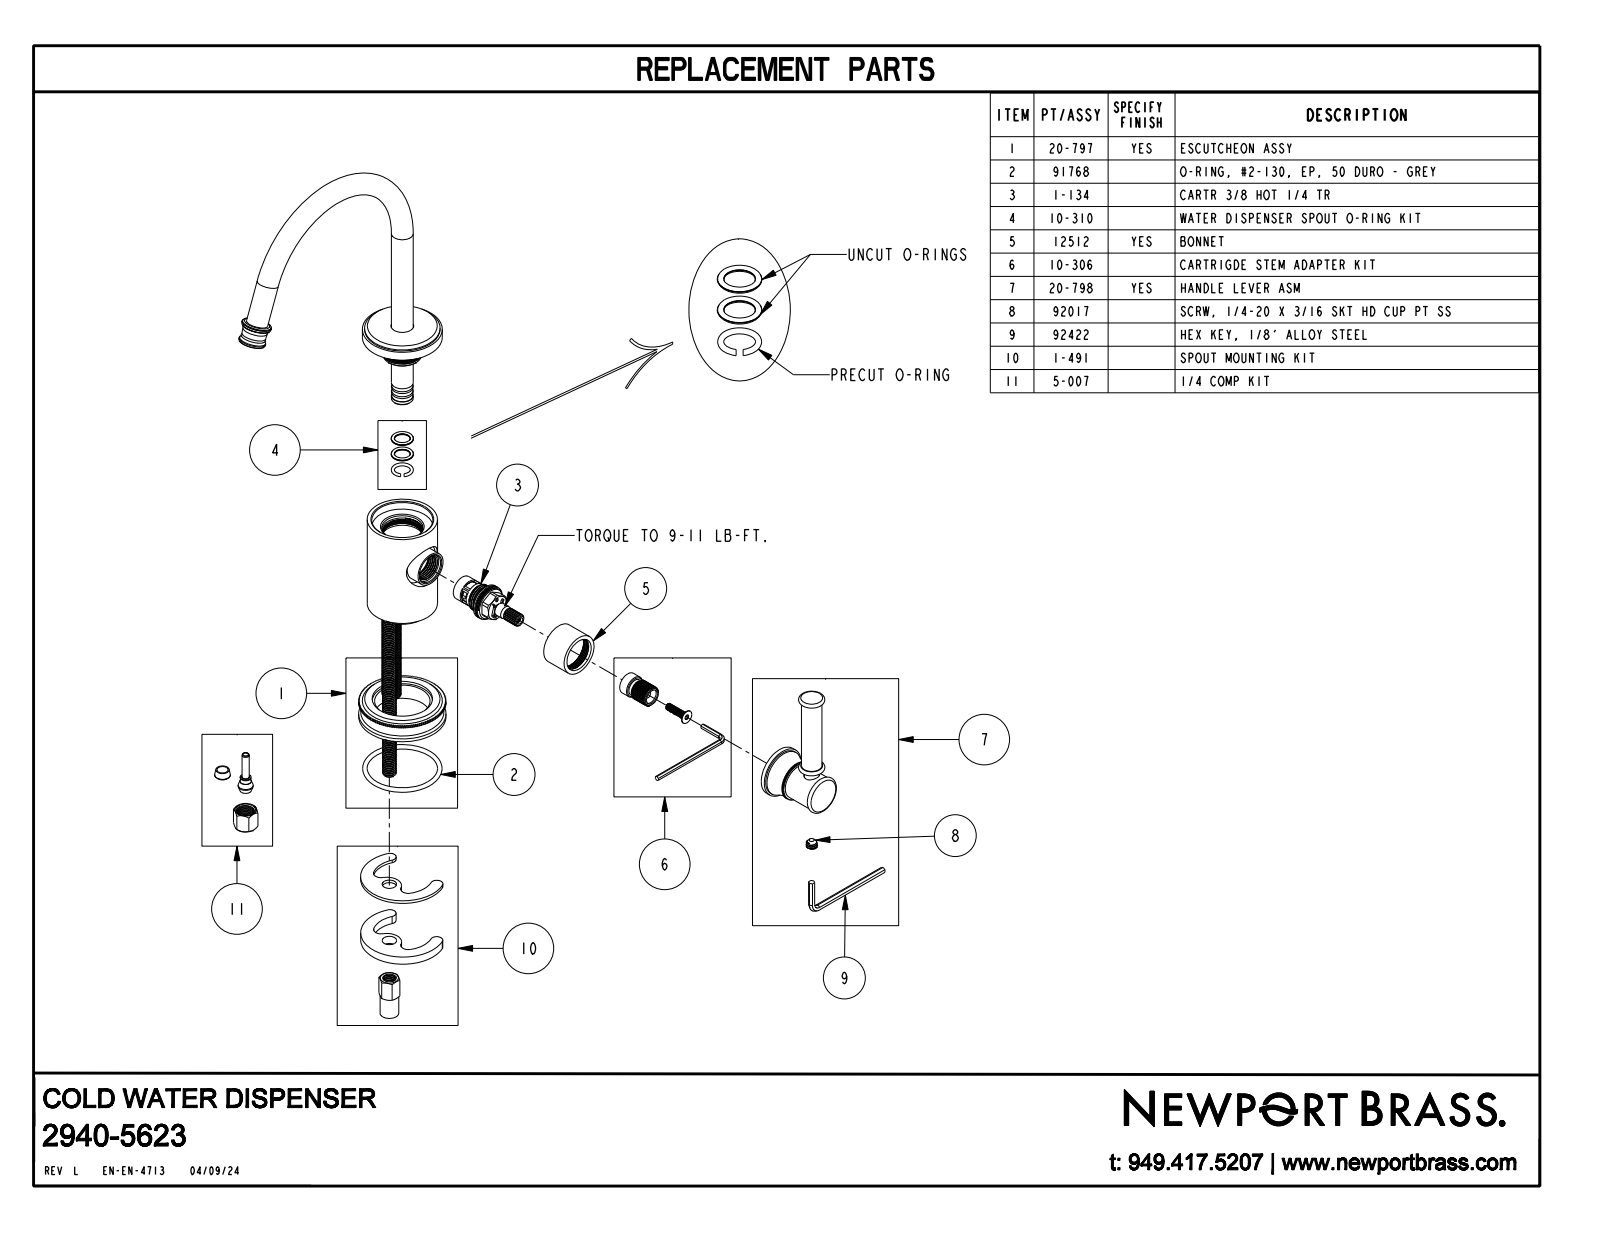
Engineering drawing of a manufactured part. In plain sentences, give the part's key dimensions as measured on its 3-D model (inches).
The part is named "2940-5623". Its 3-D file was written by "CREO PARAMETRIC BY PTC INC, 2018400 (CONFIG_CONTROL_DESIGN)". It is 1 solid with 680 faces: 408 planar, 226 cylindrical and 46 other. Overall it measures 9.52 by 6.028 by 3.551 inches. Its volume is 10.87 cubic inches and its surface area 52.95 square inches. Round holes: 1 of diameter 1. Round bosses or shafts: 2 of diameter 0.5, 1 of diameter 2, 1 of diameter 1.904, 1 of diameter 1.83, 1 of diameter 1.73, 1 of diameter 1.61, 1 of diameter 1.19, 1 of diameter 1.1. Partial cylindrical surfaces (rounded edges, fillets, slot ends): 1 of radius 0.168, 1 of radius 0.179, 1 of radius 0.47. The main face-to-face distances are 3.173, 0.445, 2.728, 0.5, 1.42, 0.055, 2.673, 2.853, 3.078, 2.408.
